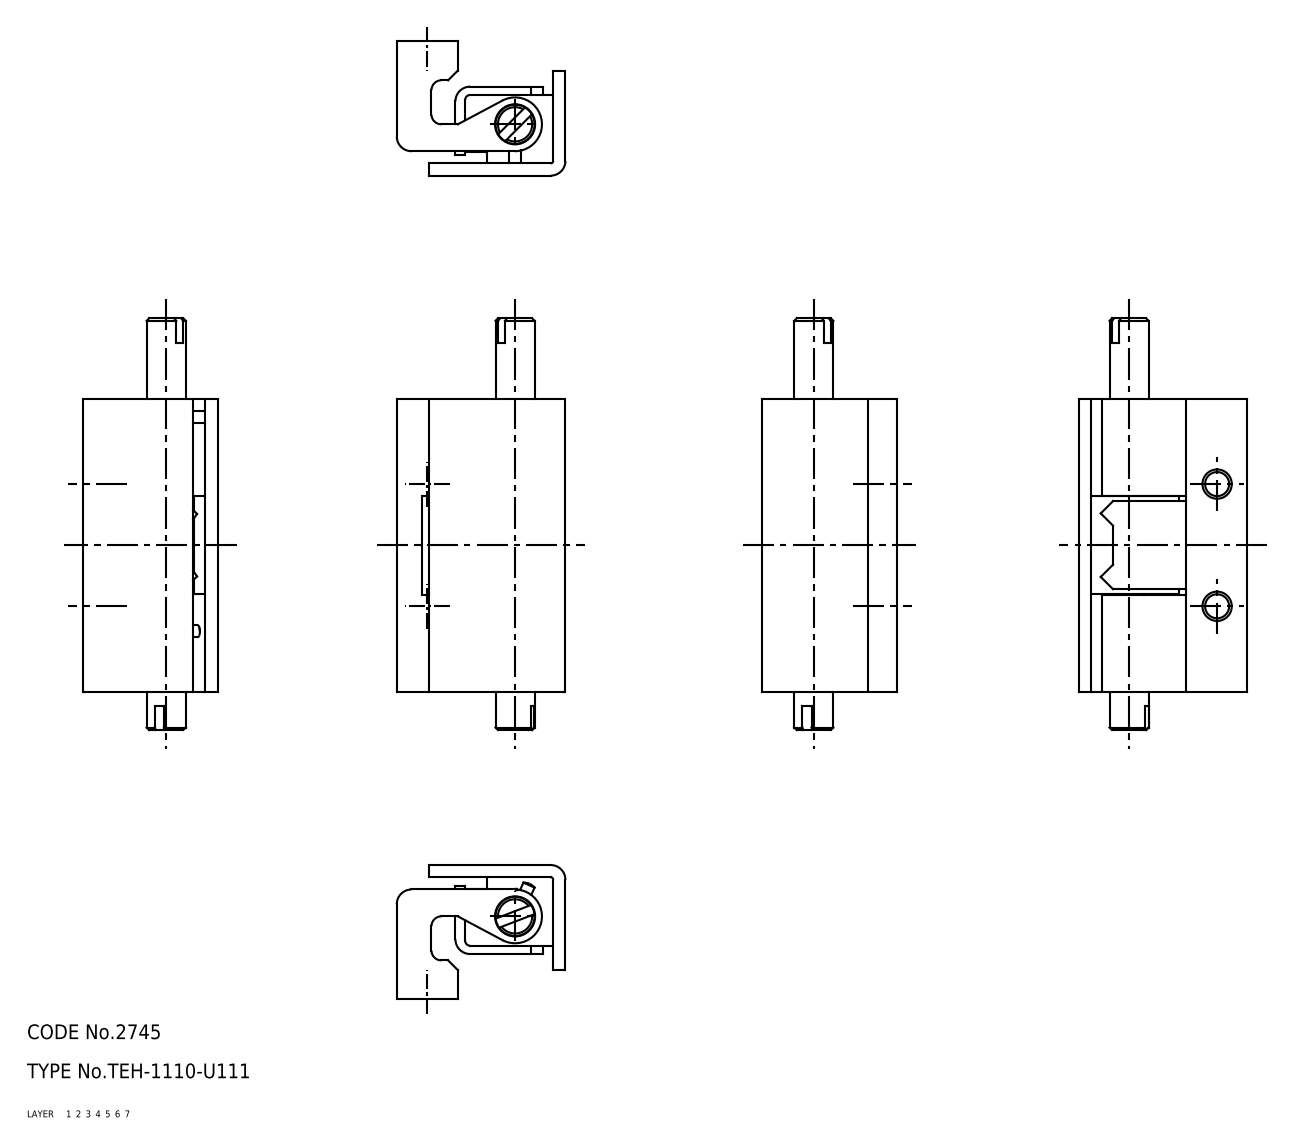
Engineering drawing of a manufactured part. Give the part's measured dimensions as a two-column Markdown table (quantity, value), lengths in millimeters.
| quantity | value |
| --- | --- |
| part name | shaft; screw; hinge pieces_B; hinge pieces_A (+2 more) |
| STEP written by | CADfix (AUTOMOTIVE_DESIGN) |
| units | millimeters |
| bodies | 6 solids, 214 faces (0 planar, 0 cylindrical, 214 other) |
| overall size | 75.6 × 34.5 × 27.5 |
| volume | 31 105 mm³ |
| surface area | 18 588 mm² |
